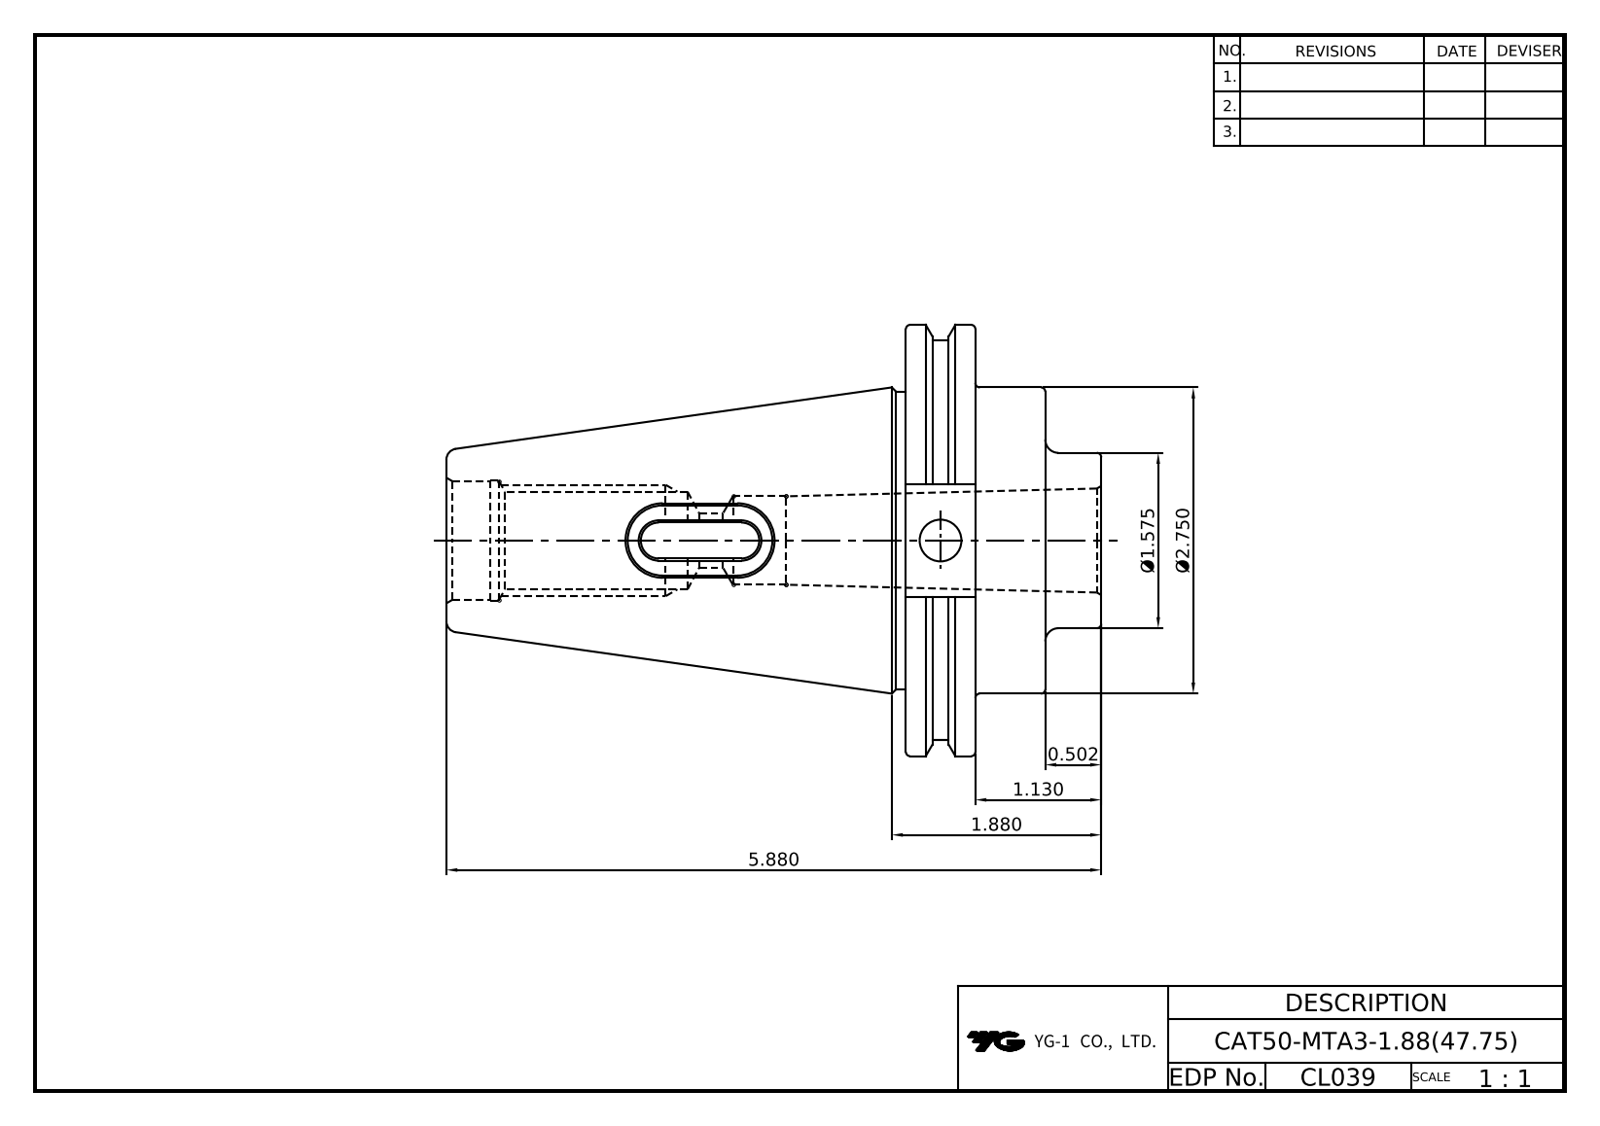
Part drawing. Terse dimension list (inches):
name: LO-CAT50-MTA3-47.75
written by: Autodesk Inventor 2025 (AUTOMOTIVE_DESIGN)
unit: in
bodies: 1 solid, 101 faces (41 planar, 23 cylindrical, 37 other)
size: 5.88 × 3.875 × 3.728
volume: 23 in³; area: 80.68 in²
holes: 1× ⌀0.375, 1× ⌀0.795, 1× ⌀0.865, 1× ⌀1.031
bosses: 1× ⌀3.875, 1× ⌀3.594, 1× ⌀2.75, 1× ⌀2.726, 1× ⌀1.575
rounds: 2× R0.156, 2× R0.315, 1× R0.246
face distances: 0.625, 1.253, 0.628, 1.755, 1.13, 0.502, 0.354, 0.665, 0.311, 4.125
